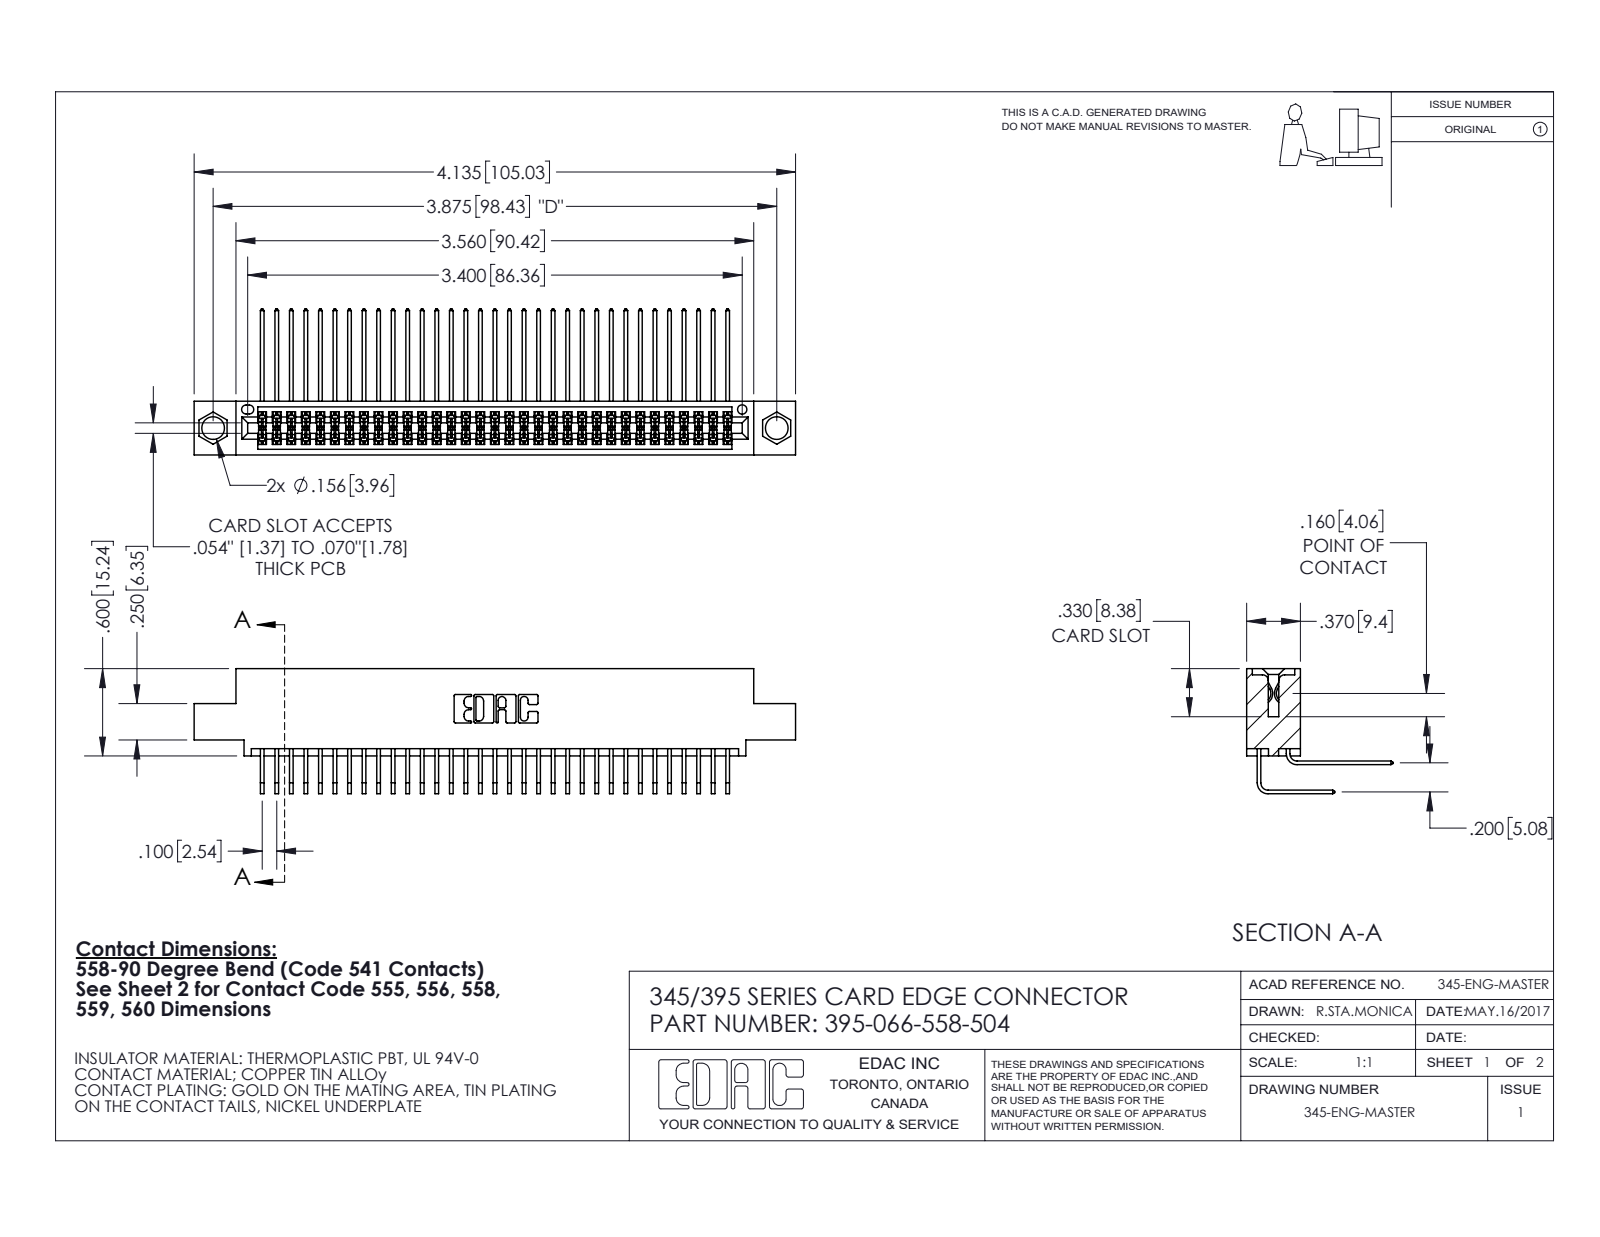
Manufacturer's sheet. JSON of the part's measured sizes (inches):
{"part_name": "395-066-558-504; 345-292-001_558 Tail - 2; 345-292-001_558 559 Tail - 1; 345 Part_0.110 Offset - 0.156 Dia-TI", "step_written_by": "SolidWorks 2020 (CONFIG_CONTROL_DESIGN)", "units": "inches", "bodies": {"solids": 67, "faces": 3576, "planar": 2408, "cylindrical": 1168, "other": 0}, "overall_size": [4.135, 1.005, 0.859], "volume_in3": 0.63, "surface_area_in2": 26.06, "round_holes": [[0.156, 2], [0.064, 1]], "partial_cylinders_radius": [[0.006, 99], [0.01, 22], [0.007, 6], [0.031, 6], [0.026, 3], [0.014, 2], [0.019, 2], [0.022, 2]], "face_to_face_distances": [0.072, 0.298, 0.2, 0.37, 0.098, 0.272, 0.025, 0.225, 0.025, 0.175], "hole_center_spacings": [0.27, 3.64, 3.875]}
